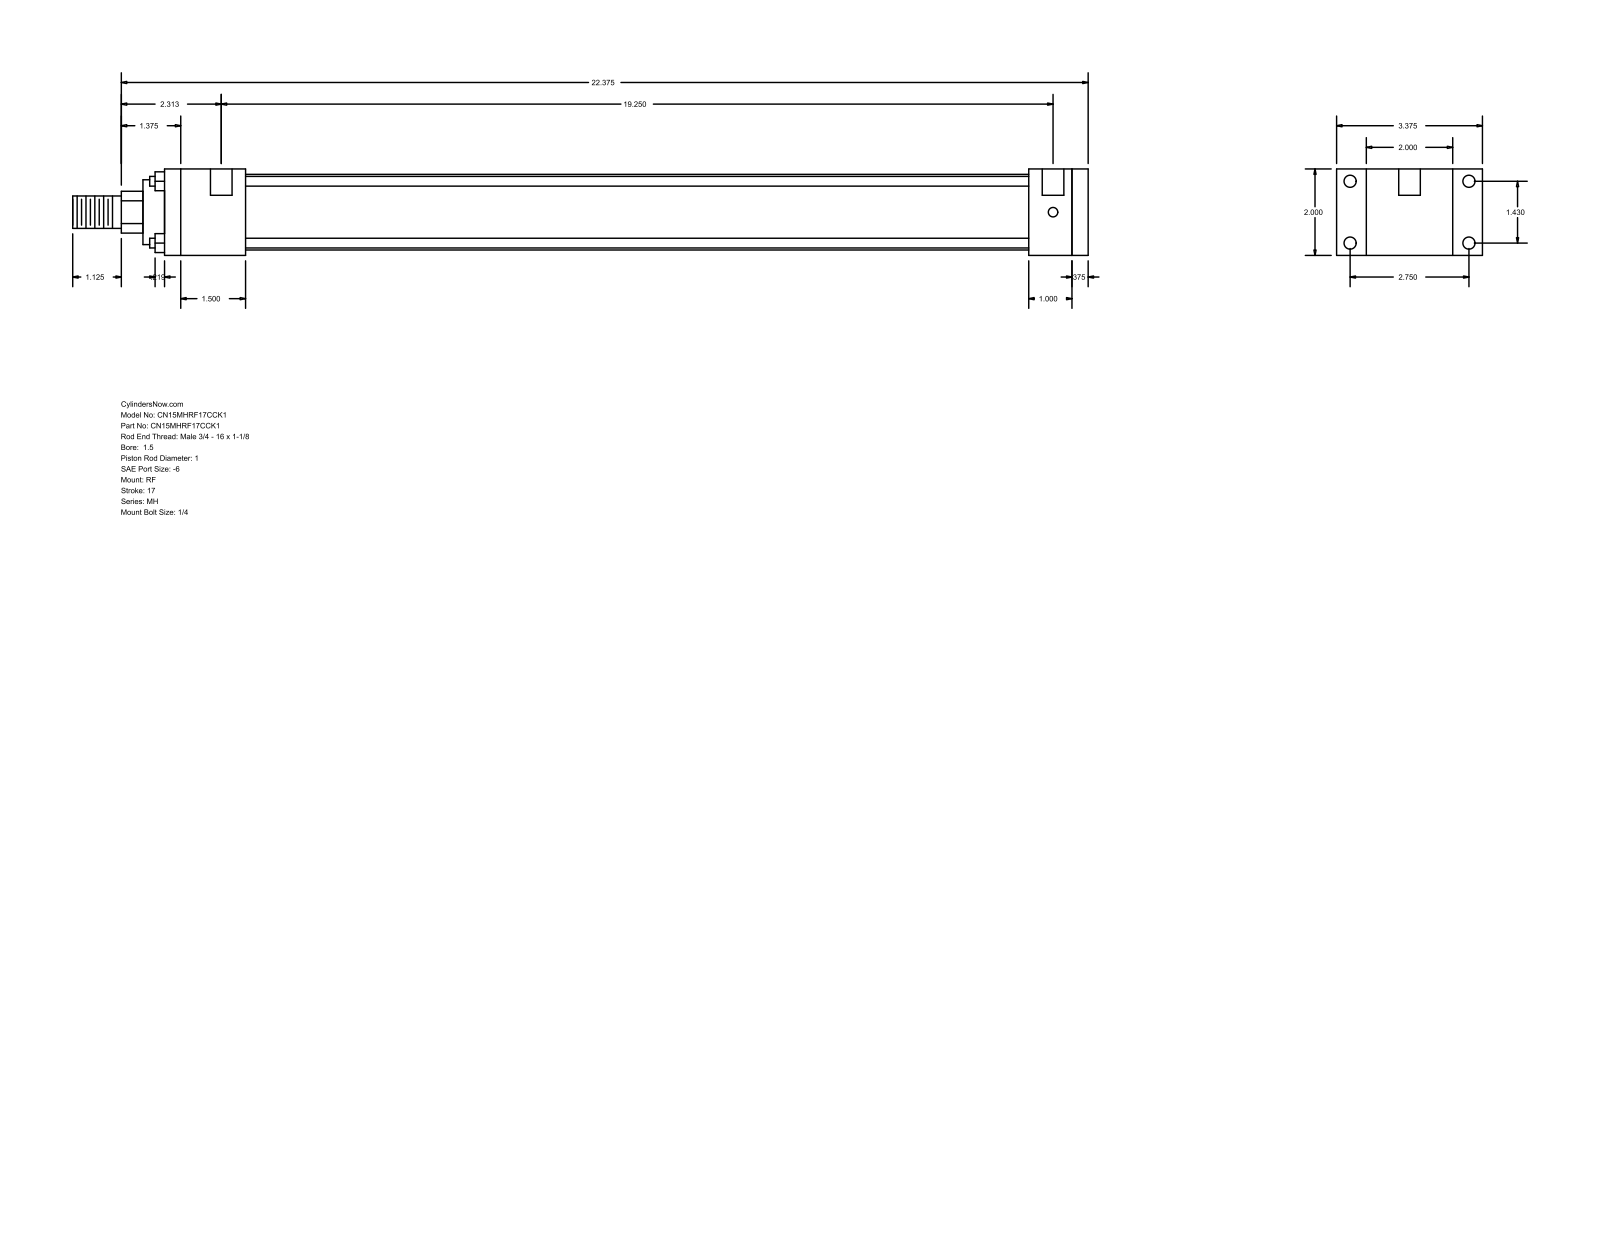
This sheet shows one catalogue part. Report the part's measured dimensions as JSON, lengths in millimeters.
{"part_name": "MH_RF__0150_1", "step_written_by": "GSSL Pune (CONFIG_CONTROL_DESIGN)", "units": "millimeters", "bodies": {"solids": 0, "faces": 92, "planar": 64, "cylindrical": 28, "other": 0}, "overall_size": [596.9, 85.72, 50.8], "round_holes": [[5.56, 4], [7.14, 4], [12.7, 2]], "round_bosses_or_shafts": [[5.71, 4], [44.45, 1], [38.1, 1], [25.4, 1], [19.05, 1]], "partial_cylinders_radius": [[12.29, 1]], "face_to_face_distances": [50.8, 9.53, 533.4, 25.4, 542.93, 17.46, 68.26, 508, 34.93, 47.63], "hole_center_spacings": [36.32, 69.84, 78.72, 492.13, 3.18, 488.95]}
